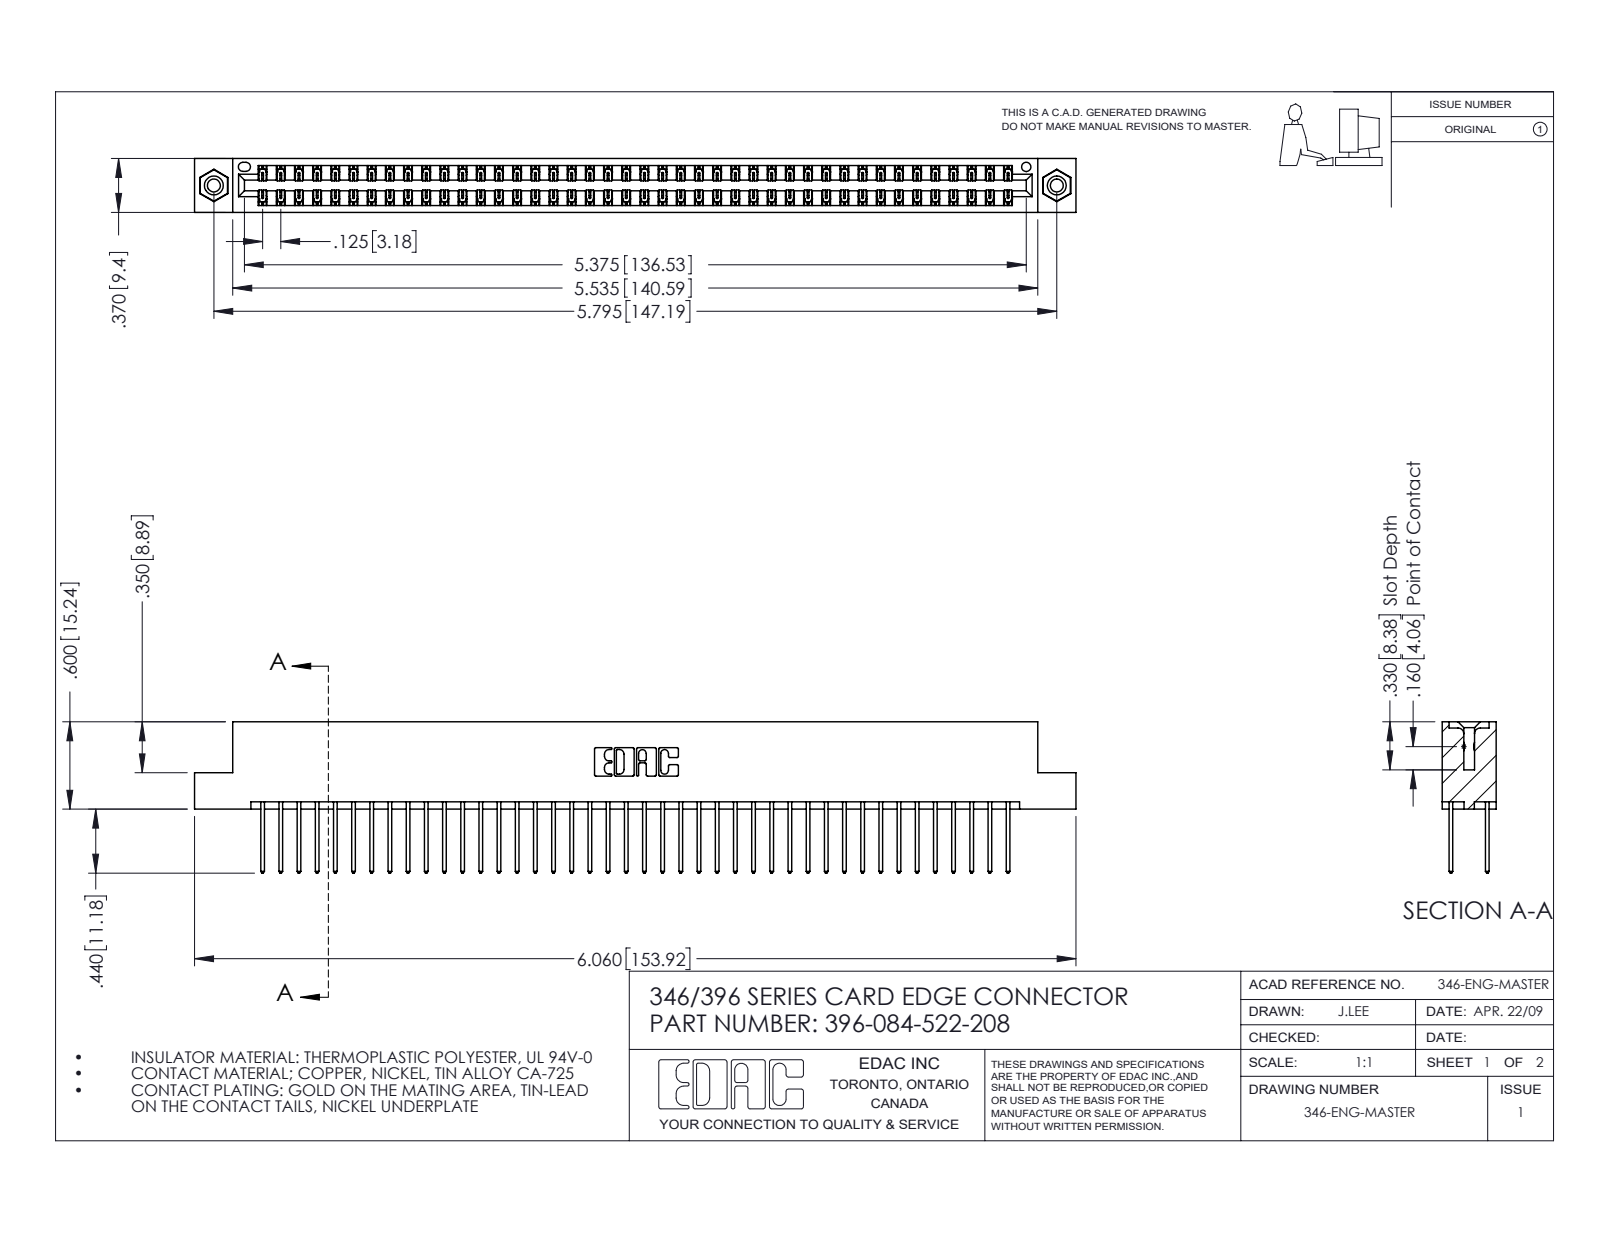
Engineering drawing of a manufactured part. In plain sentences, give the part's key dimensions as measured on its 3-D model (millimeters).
The part is named "345-292-001_345-293-122; 396-084-522-208; 346 Part_Flush Mounting Lugs - 0.156 Dia-TI; 345-250-001_345-250-003-102". Its 3-D file was written by "SolidWorks 2016 (CONFIG_CONTROL_DESIGN)". It is 87 solids with 4550 faces: 3048 planar, 1486 cylindrical and 16 other. Overall it measures 153.9 by 26.4 by 9.4 millimeters. Its volume is 15 200 cubic millimeters and its surface area 21 940 square millimeters. Round holes: 2 of diameter 2.3, 2 of diameter 3.2, 2 of diameter 4, 1 of diameter 1.6. Round bosses or shafts: 2 of diameter 3.9. Partial cylindrical surfaces (rounded edges, fillets, slot ends): 126 of radius 0.2, 84 of radius 0.3, 22 of radius 0.3, 6 of radius 0.2, 6 of radius 0.8, 3 of radius 0.7, 2 of radius 0.4, 2 of radius 0.6. The main face-to-face distances are 1.2, 8.2, 6.4, 9.4, 1.8, 7.6, 0.6, 7, 3.8, 5.6. The hole center spacings are 6.2, 141.9, 147.2.
